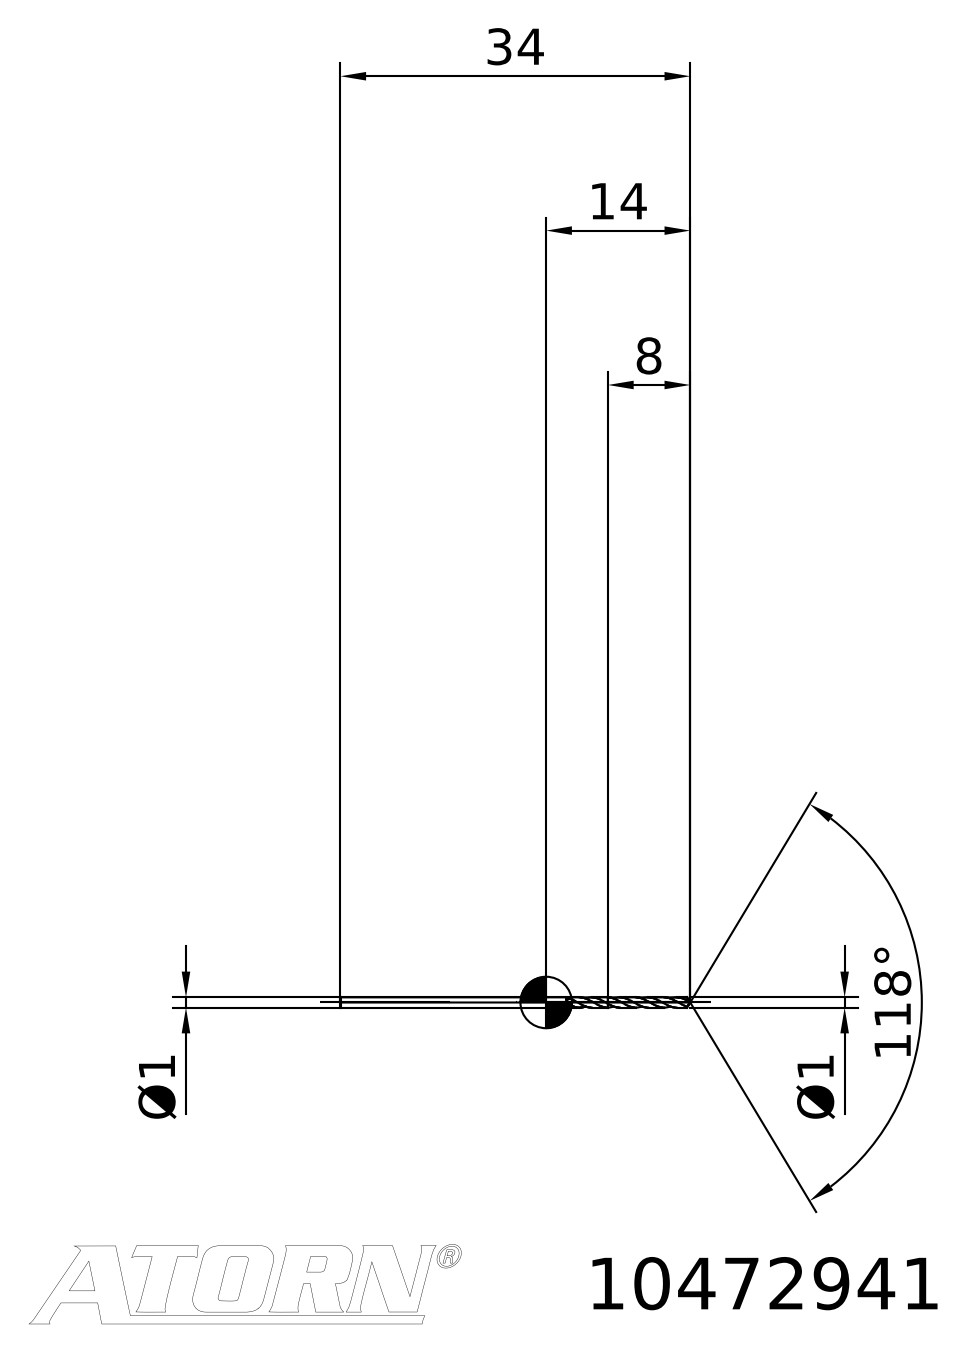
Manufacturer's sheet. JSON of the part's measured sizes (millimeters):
{"step_written_by": "TDM (AUTOMOTIVE_DESIGN)", "units": "millimeters", "bodies": {"solids": 2, "faces": 26, "planar": 3, "cylindrical": 0, "other": 23}, "overall_size": [34, 2.48, 1], "volume_mm3": 23, "surface_area_mm2": 112, "face_to_face_distances": [26]}
